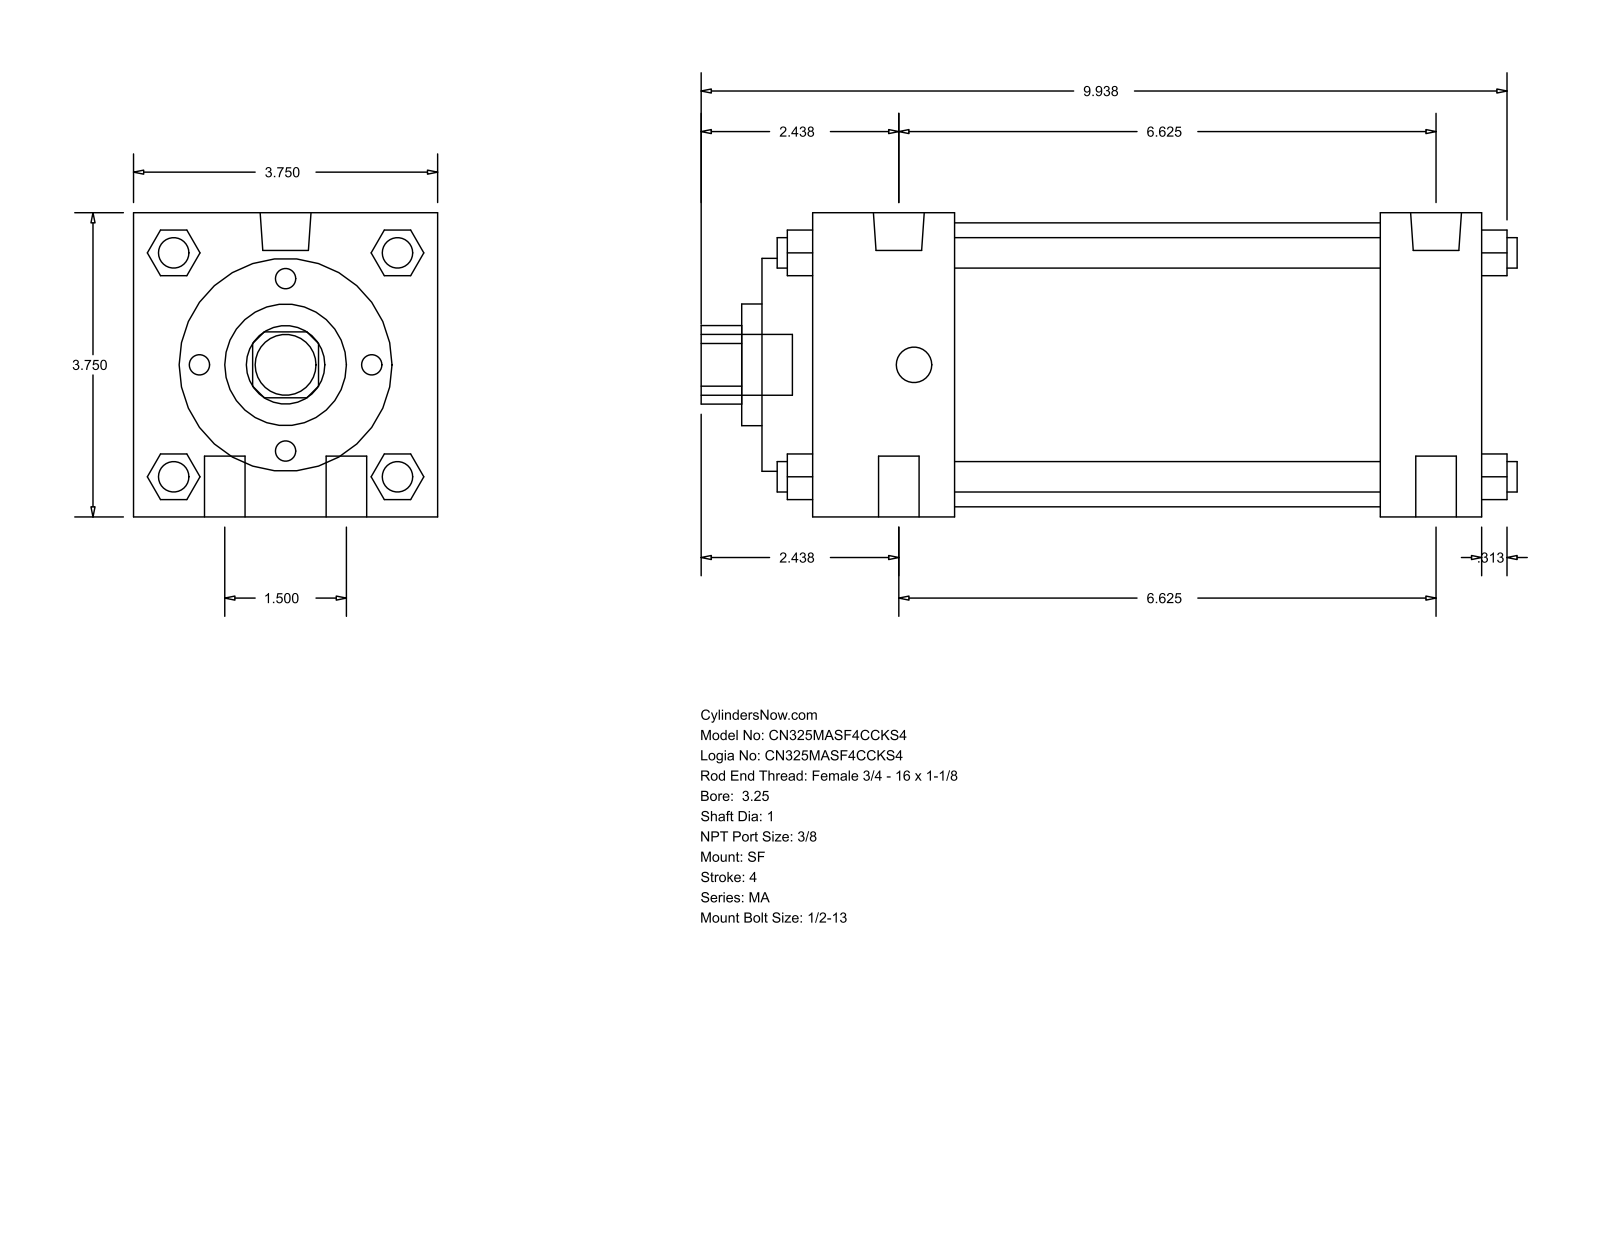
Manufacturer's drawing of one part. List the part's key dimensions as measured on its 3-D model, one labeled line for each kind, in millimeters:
Part name (STEP PRODUCT): MA_SF__0325_1
STEP written by: GSSL Pune (CONFIG_CONTROL_DESIGN)
Units: millimetres
Bodies: 0 solids, 126 faces (95 planar, 31 cylindrical, 0 other)
Overall size (bounding box): 255.59 × 95.25 × 95.25
Round holes (diameter × count): ⌀25.4 ×1, ⌀38.1 ×1, ⌀66.67 ×1, ⌀88.9 ×1
Round bosses / shafts (diameter × count): ⌀12.7 ×4, ⌀9.53 ×4, ⌀15.93 ×2, ⌀11.11 ×2, ⌀19.05 ×1
Partial cylindrical surfaces — rounded edges, fillets, slot ends (radius × count): R12.29 ×1
Main face-to-face distances: 95.24, 209.55, 225.42, 15.87, 177.8, 31.75, 44.46, 133.34, 165.09, 60.33
